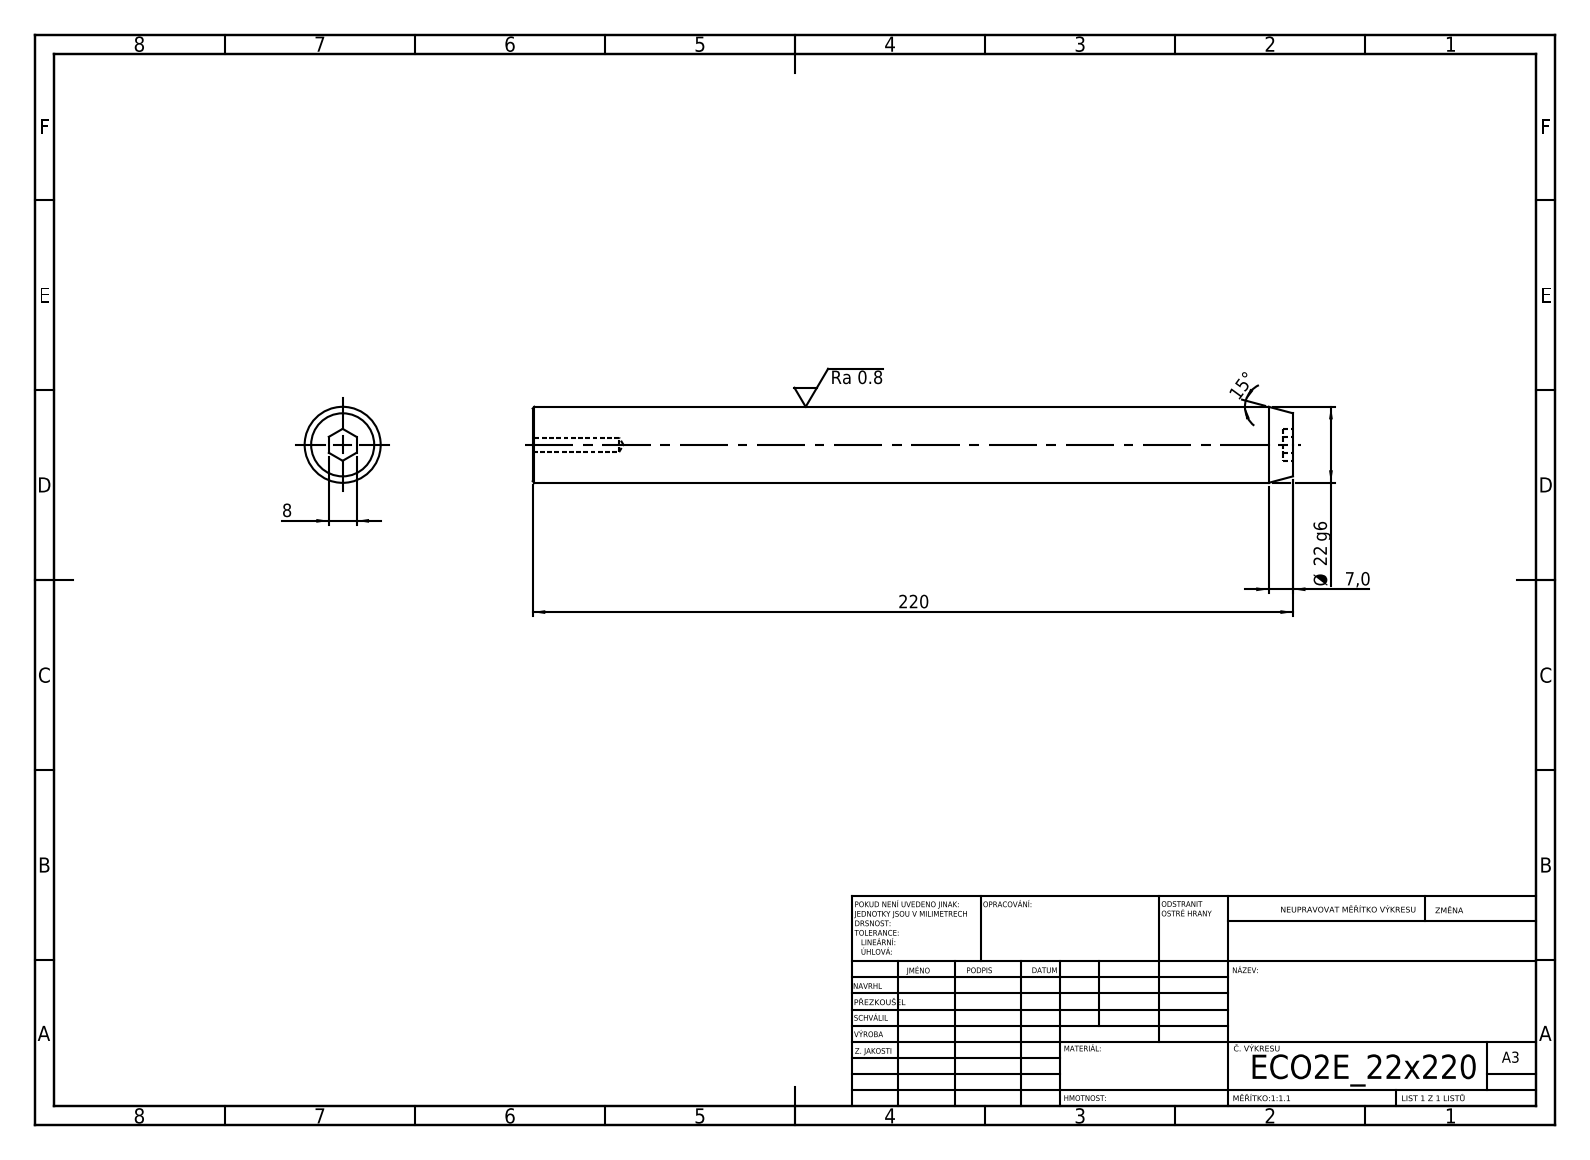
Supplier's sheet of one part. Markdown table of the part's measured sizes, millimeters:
| quantity | value |
| --- | --- |
| STEP written by | SolidWorks 2019 (CONFIG_CONTROL_DESIGN) |
| units | millimeters |
| bodies | 1 solid, 19 faces (9 planar, 4 cylindrical, 6 other) |
| overall size | 220 × 22 × 22 |
| volume | 82 685 mm³ |
| surface area | 16 211 mm² |
| round holes (diameter × count) | 4.2 × 1 |
| round bosses / shafts (diameter × count) | 22 × 1 |
| main face-to-face distances | 220, 2.8, 217.2, 8 |
